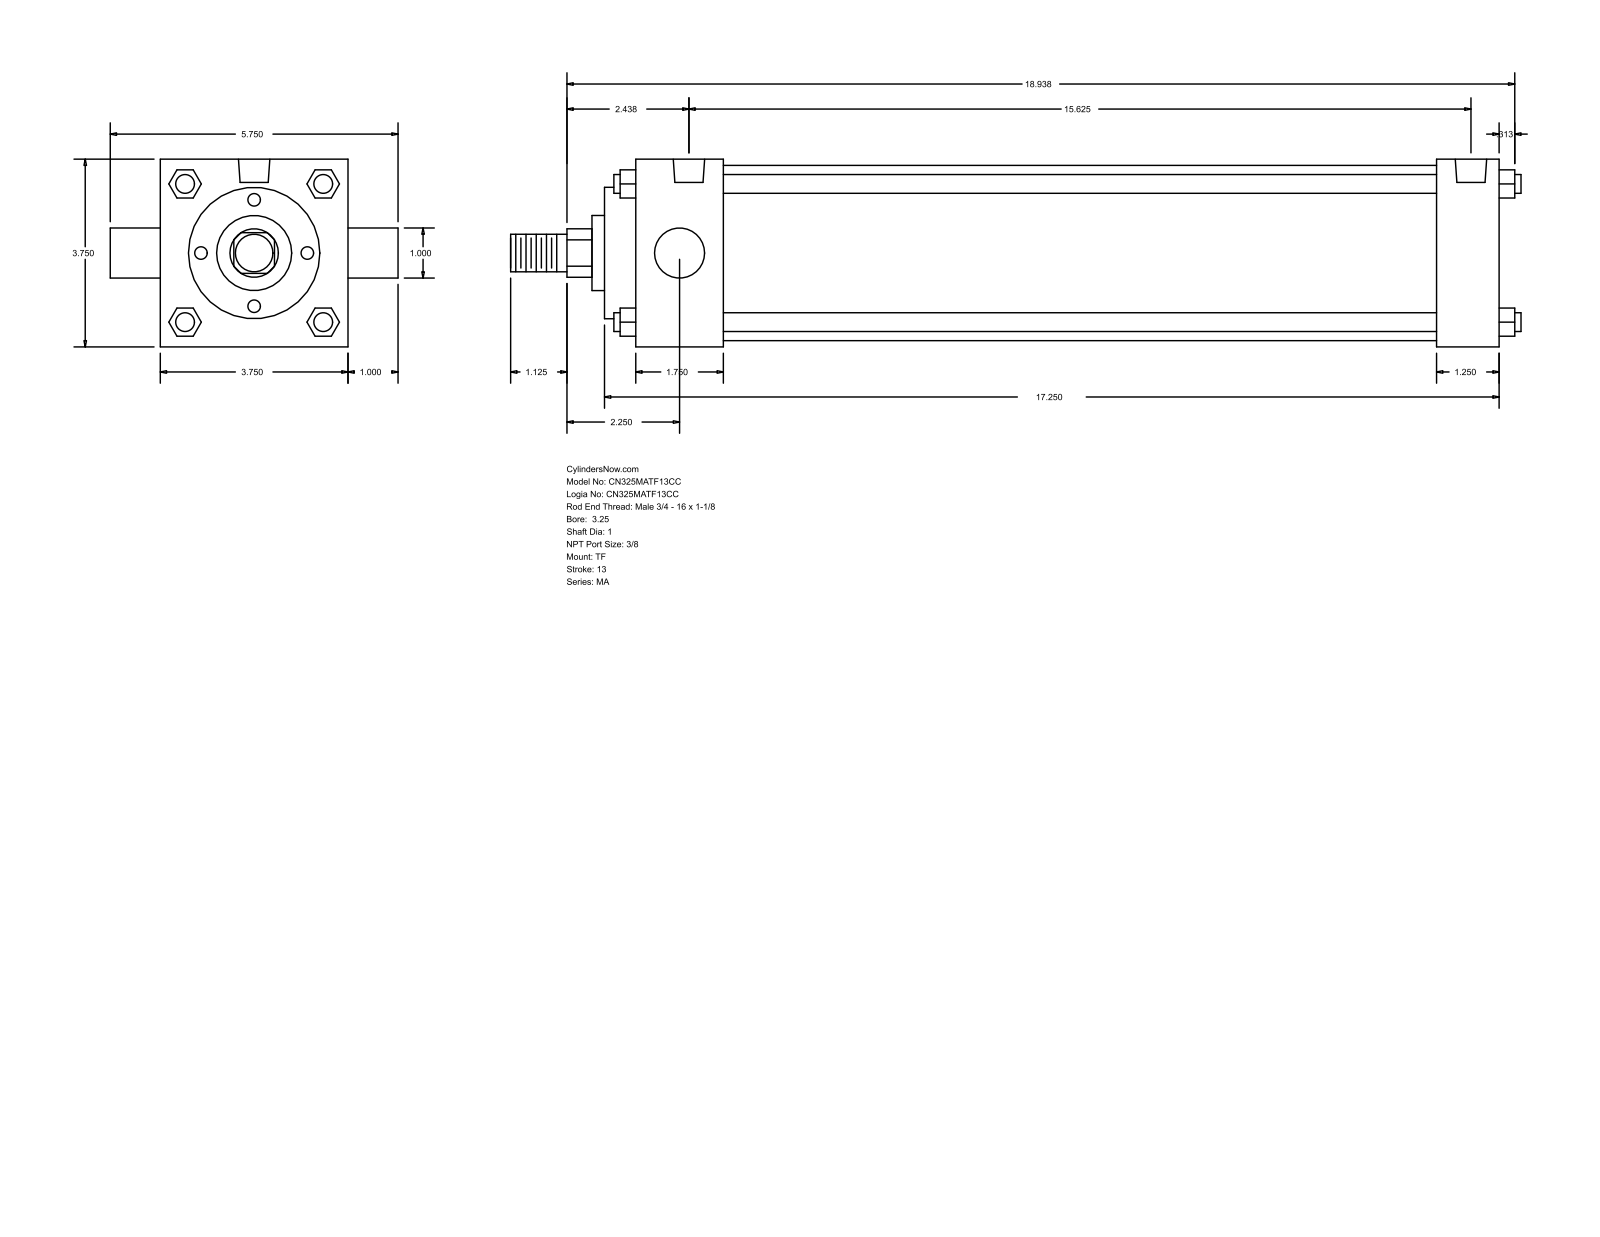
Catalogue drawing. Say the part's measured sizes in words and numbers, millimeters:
The part is named "MA_TF__0325_1". Its 3-D file was written by "GSSL Pune (CONFIG_CONTROL_DESIGN)". It is 0 solids with 122 faces: 93 planar, 29 cylindrical and 0 other. Overall it measures 512.76 by 146.05 by 95.25 millimeters. Round holes: 3 of diameter 11.11, 2 of diameter 15.93. Round bosses or shafts: 4 of diameter 9.53, 2 of diameter 25.4, 1 of diameter 88.9, 1 of diameter 66.67, 1 of diameter 38.1, 1 of diameter 19.05. Partial cylindrical surfaces (rounded edges, fillets, slot ends): 1 of radius 12.29. The main face-to-face distances are 95.24, 438.15, 454.02, 44.46, 406.4, 361.94, 393.69, 31.75, 15.87, 60.33. The hole center spacings are 4.76, 4.77, 387.35, 392.11, 392.12, 396.88.
